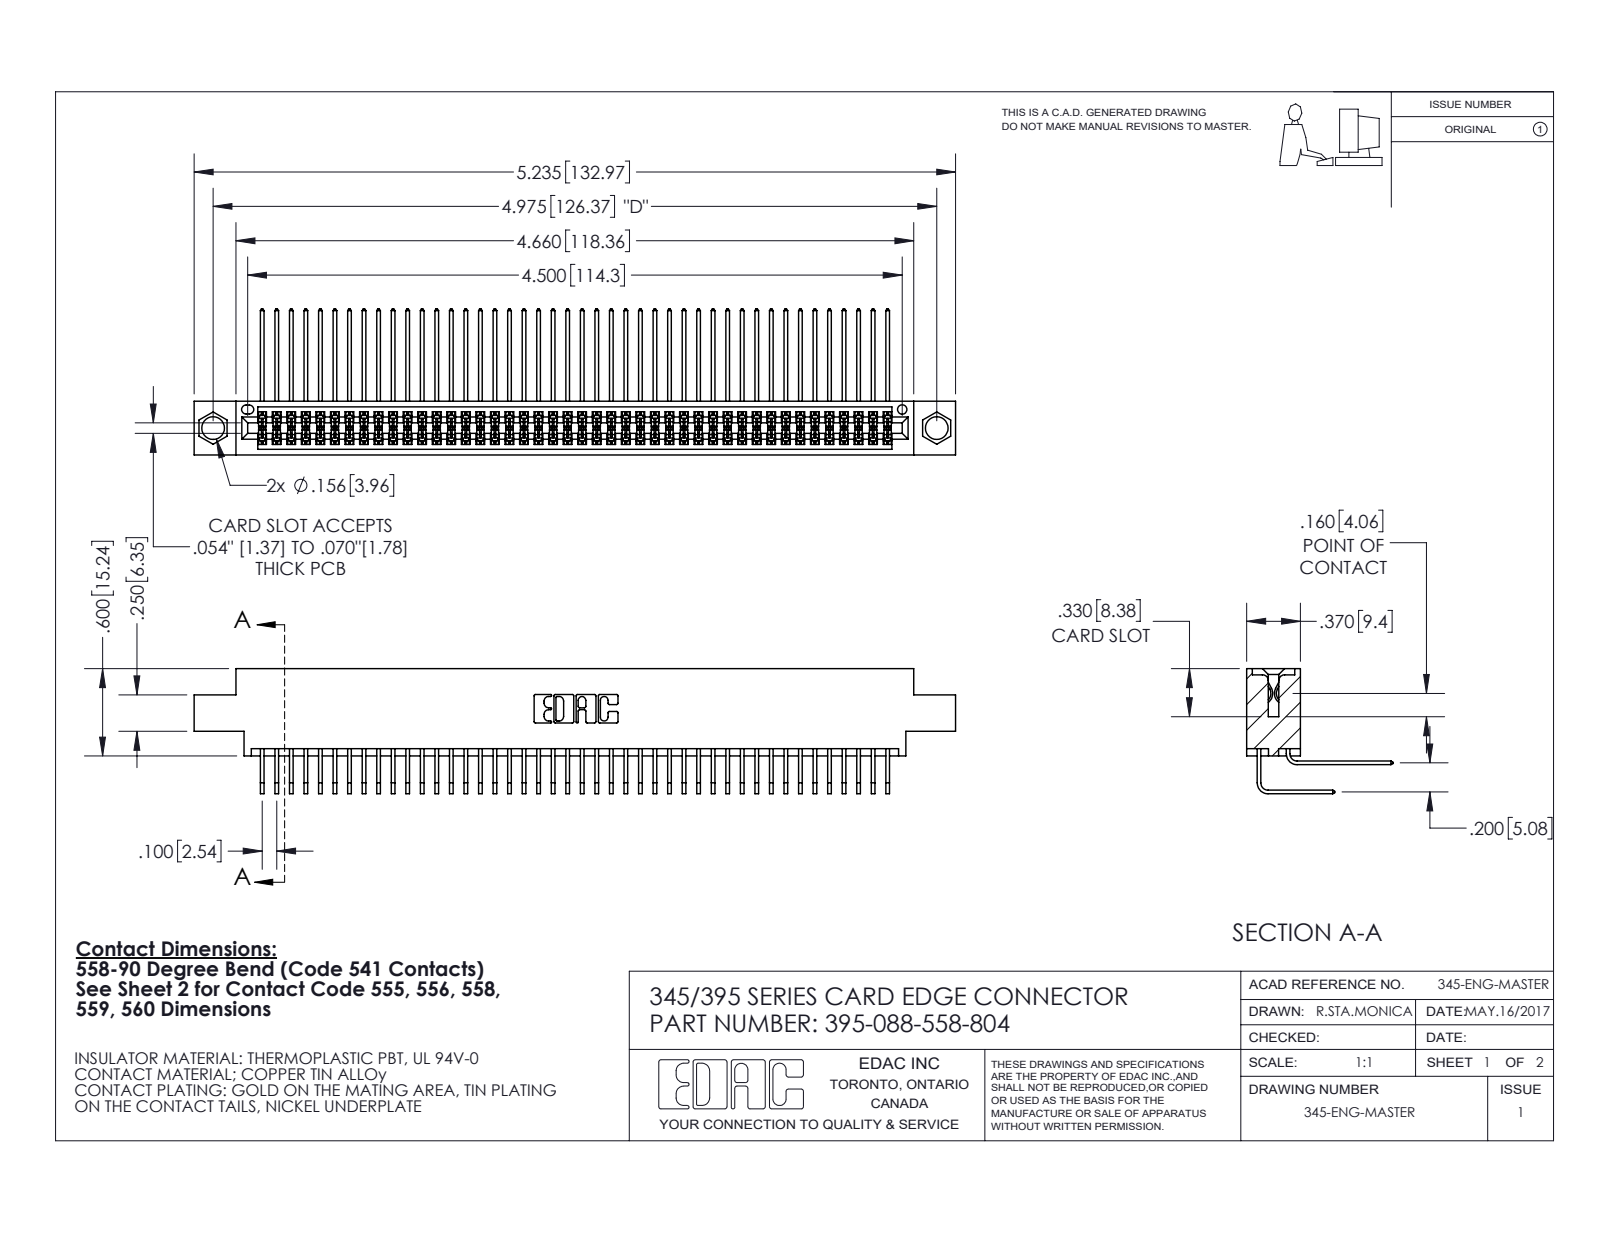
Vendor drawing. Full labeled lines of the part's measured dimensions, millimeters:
Part name (STEP PRODUCT): 345-292-001_558 Tail - 2; 345 Part_0.170 Offset - 0.156 Dia-TI; 345-292-001_558 559 Tail - 1; 395-088-558-804
STEP written by: SolidWorks 2020 (CONFIG_CONTROL_DESIGN)
Units: millimetres
Bodies: 89 solids, 4720 faces (3178 planar, 1542 cylindrical, 0 other)
Overall size (bounding box): 133 × 25.5 × 21.8
Volume: 13 200 mm³ · Surface area: 21 970 mm²
Round holes (diameter × count): ⌀4 ×2, ⌀1.6 ×1
Partial cylindrical surfaces — rounded edges, fillets, slot ends (radius × count): R0.2 ×176, R0.3 ×22, R0.2 ×6, R0.8 ×6, R0.7 ×3, R0.4 ×2, R0.5 ×2, R0.6 ×2
Main face-to-face distances: 1.8, 7.6, 5.1, 9.4, 2.5, 6.9, 0.6, 5.7, 4.4, 0.6
Hole centre spacings: 6.9, 120.4, 126.4
